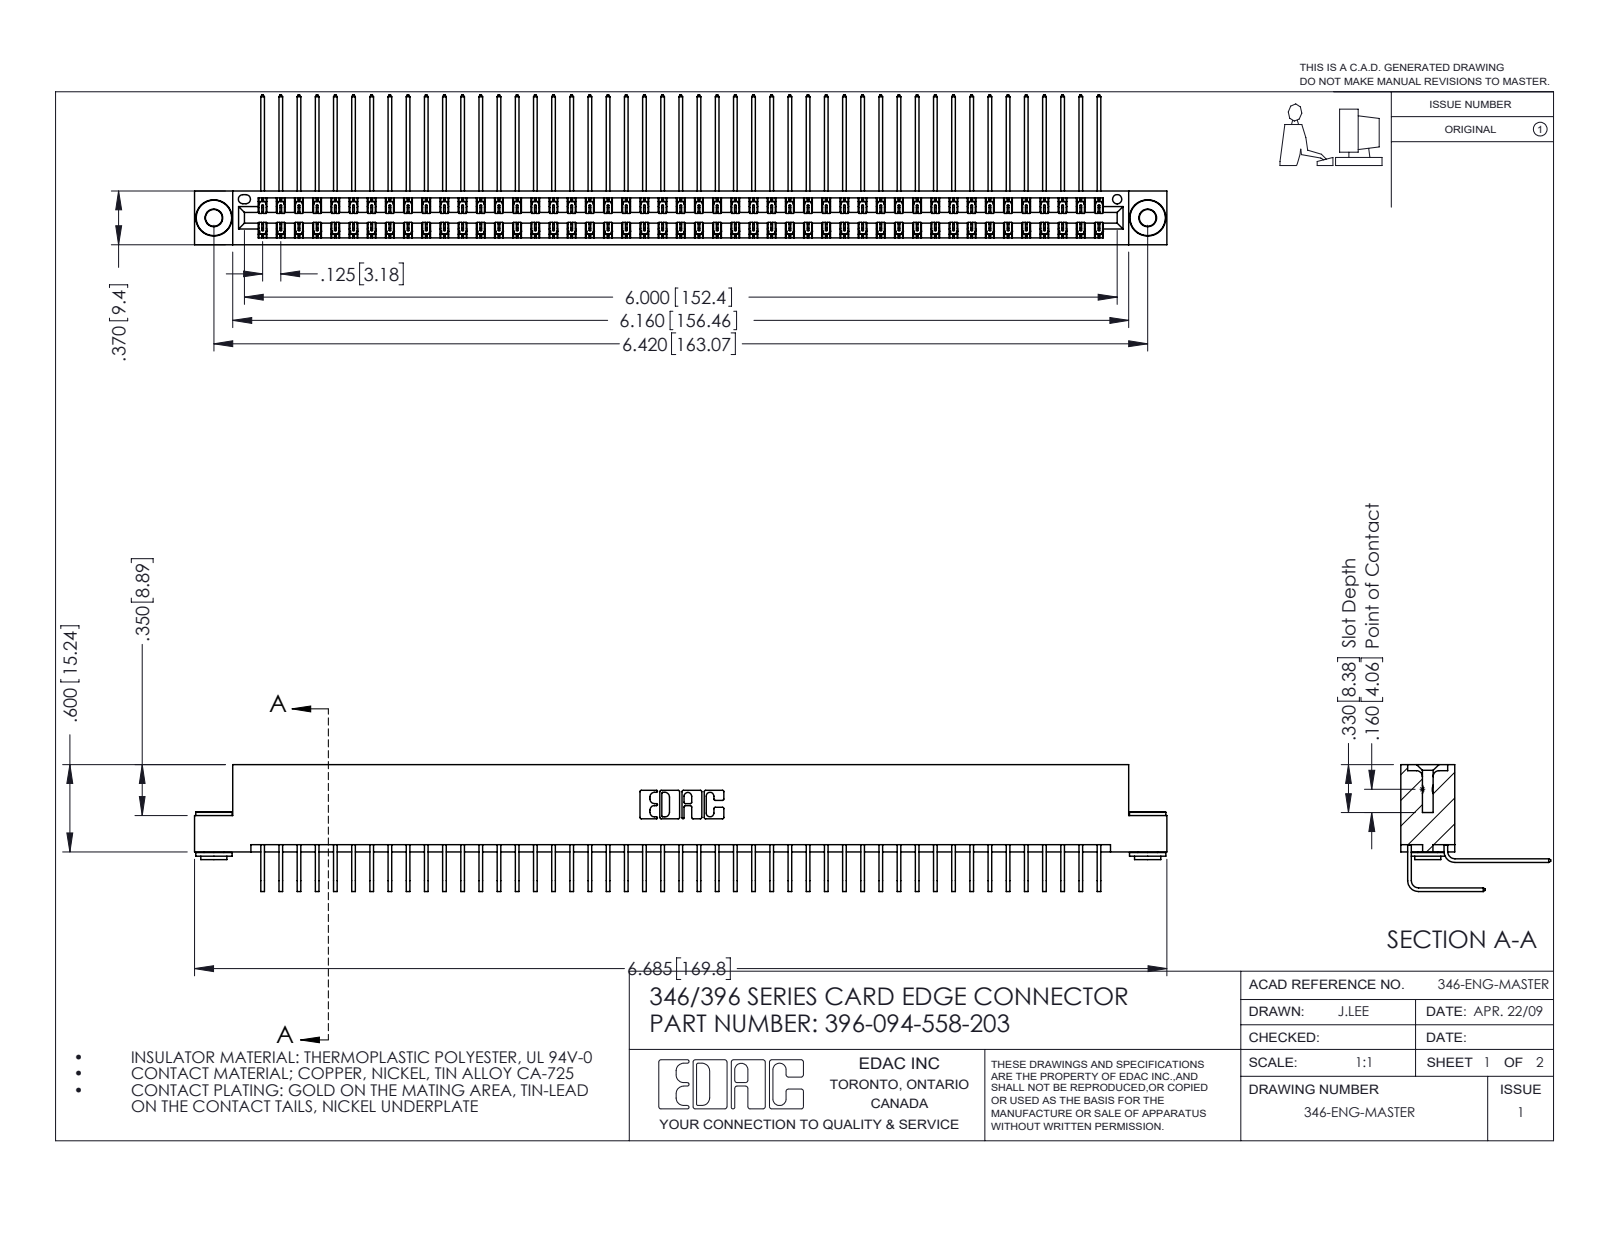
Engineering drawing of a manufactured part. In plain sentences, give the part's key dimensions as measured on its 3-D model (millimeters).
The part is named "345-250-002_345-250-002-102; 345-292-001_558 Tail - 2; 396-094-558-203; 345-292-001_558 559 Tail - 1 (+1 more)". Its 3-D file was written by "SolidWorks 2016 (CONFIG_CONTROL_DESIGN)". It is 97 solids with 5236 faces: 3564 planar, 1664 cylindrical and 8 other. Overall it measures 169.8 by 26.2 by 22.2 millimeters. Its volume is 17 160 cubic millimeters and its surface area 26 480 square millimeters. Round holes: 2 of diameter 2.9, 2 of diameter 4, 1 of diameter 1.6. Round bosses or shafts: 2 of diameter 6.4, 2 of diameter 4.6, 2 of diameter 3.5. Partial cylindrical surfaces (rounded edges, fillets, slot ends): 141 of radius 0.2, 22 of radius 0.3, 6 of radius 0.2, 6 of radius 0.8, 3 of radius 0.7, 2 of radius 0.4, 2 of radius 0.6, 2 of radius 0.6. The main face-to-face distances are 8.2, 1.2, 0.6, 6.4, 9.4, 7.6, 1.8, 7, 3.8, 5.6. The hole center spacings are 6.2, 157.8, 163.1.
